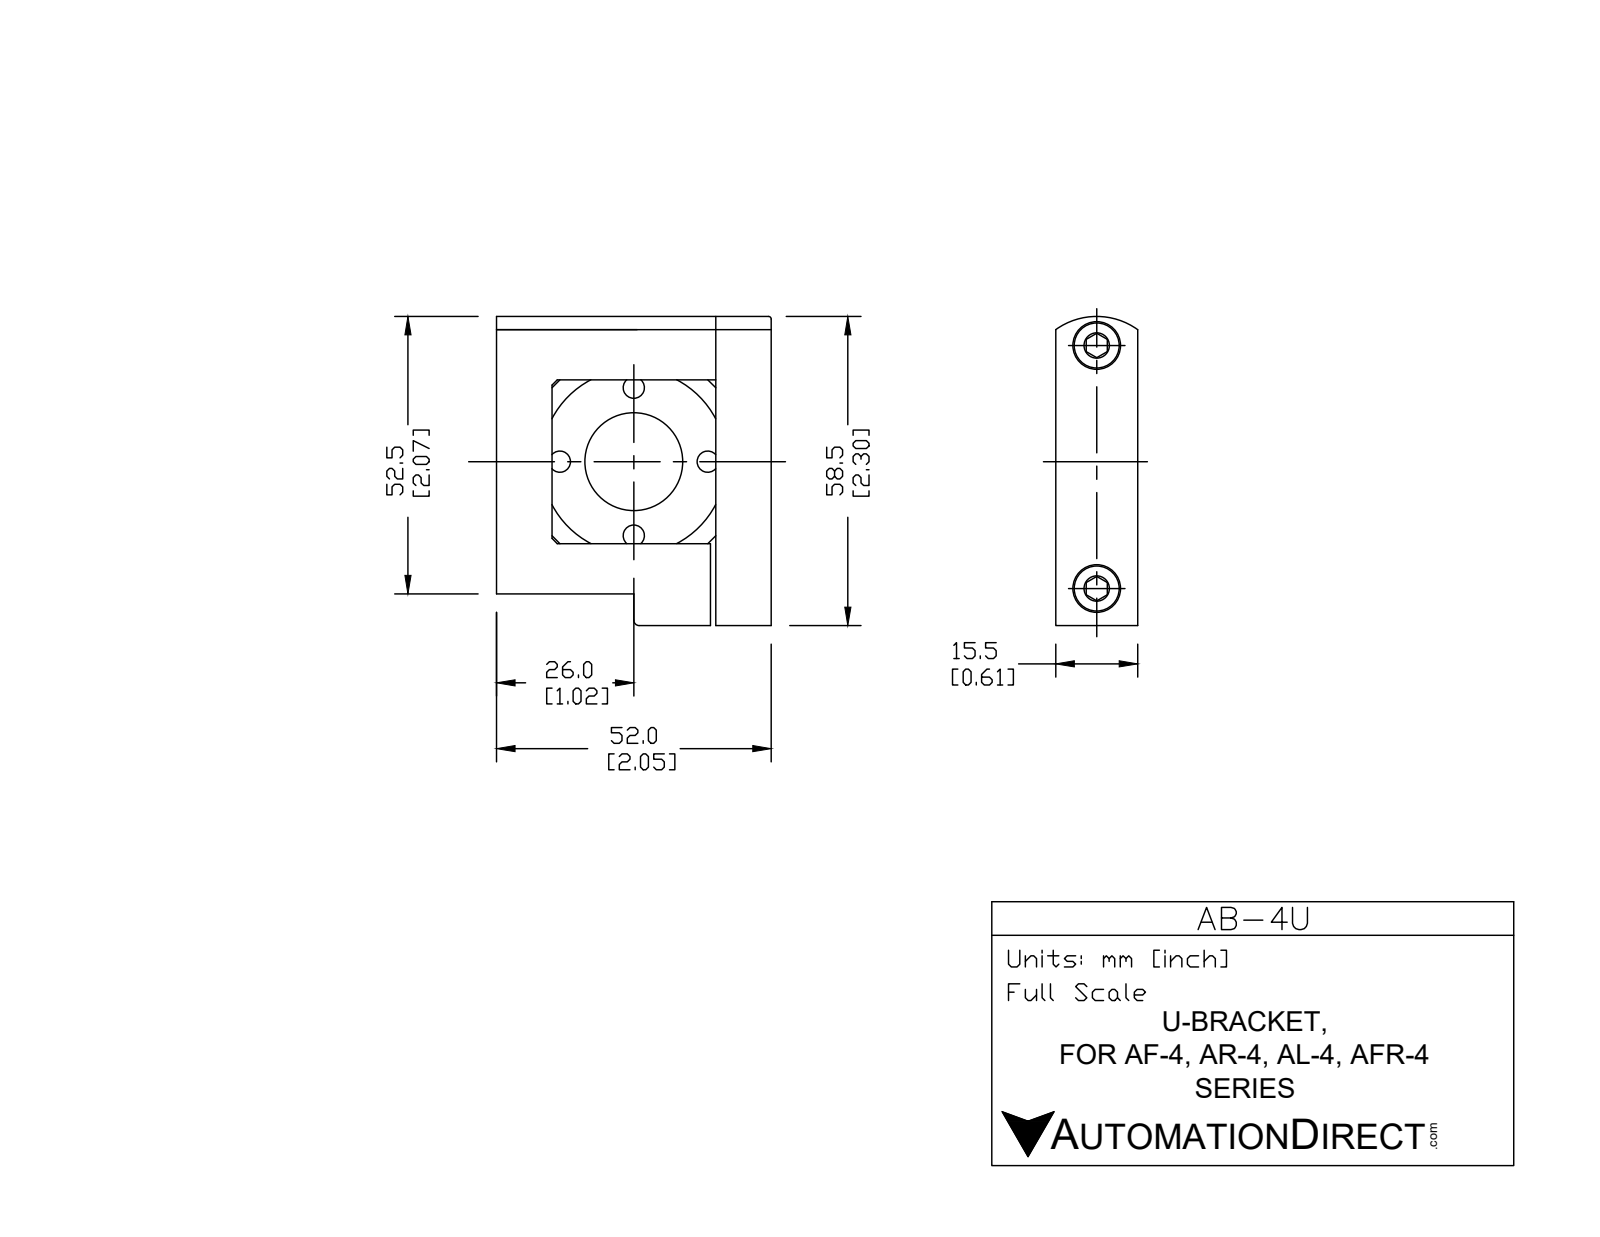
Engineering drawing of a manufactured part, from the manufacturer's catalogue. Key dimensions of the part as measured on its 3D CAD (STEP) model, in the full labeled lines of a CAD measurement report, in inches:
Part name (STEP PRODUCT): AB-4U
STEP written by: SolidWorks 2015 (CONFIG_CONTROL_DESIGN)
Units: inches
Bodies: 3 solids, 92 faces (60 planar, 20 cylindrical, 12 other)
Overall size (bounding box): 2.303 × 2.047 × 0.61
Volume: 1.709 in³ · Surface area: 20.46 in²
Round holes (diameter × count): ⌀0.217 ×2, ⌀0.33 ×2, ⌀0.728 ×1
Round bosses / shafts (diameter × count): ⌀0.305 ×2, ⌀0.157 ×2
Partial cylindrical surfaces — rounded edges, fillets, slot ends (radius × count): R0.059 ×1, R0.522 ×1
Main face-to-face distances: 0.61, 0.098, 2.047, 1.319, 0.315, 0.108, 0.502, 1.732, 0.283, 0.327
Hole centre spacings: 1.811
